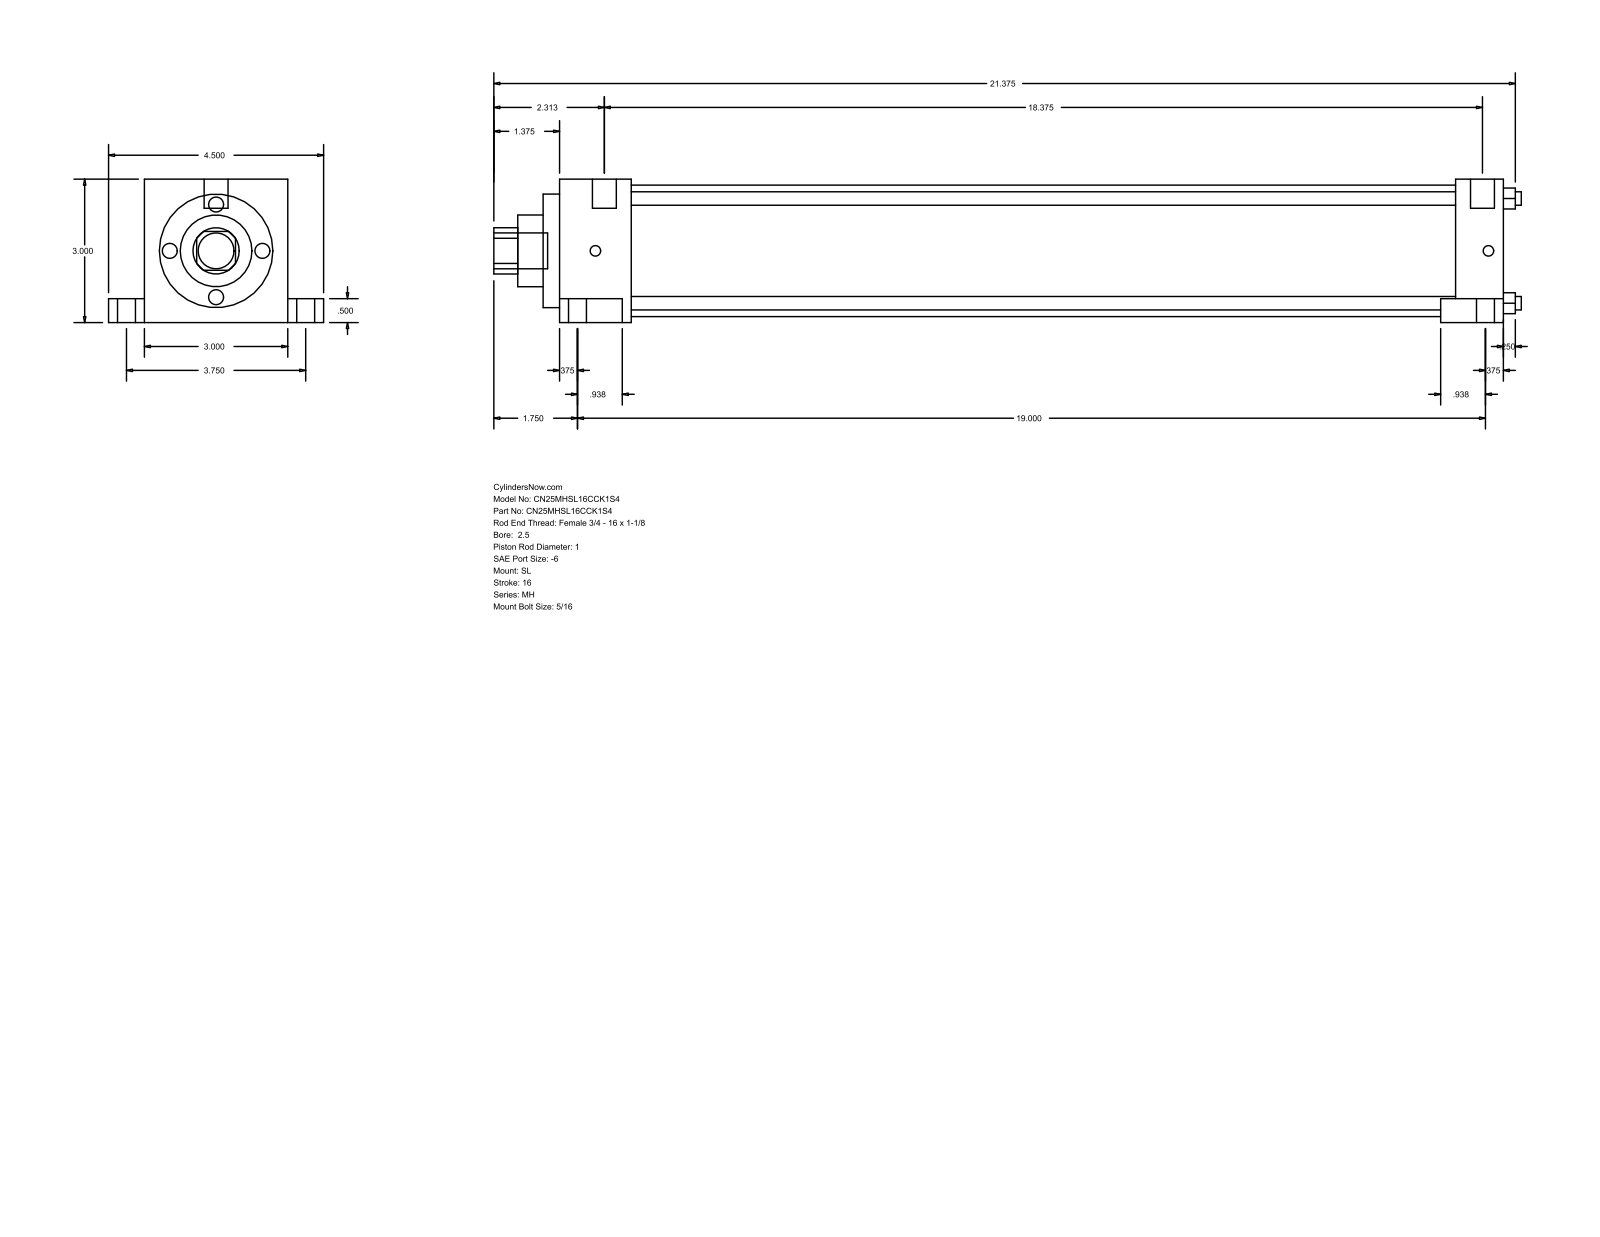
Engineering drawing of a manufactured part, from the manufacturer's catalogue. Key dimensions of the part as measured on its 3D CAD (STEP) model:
Part name (STEP PRODUCT): MH_SL__0250_1
STEP written by: GSSL Pune (CONFIG_CONTROL_DESIGN)
Units: millimetres
Bodies: 0 solids, 86 faces (61 planar, 25 cylindrical, 0 other)
Overall size (bounding box): 546.1 × 114.3 × 76.2
Round holes (diameter × count): ⌀7.14 ×4, ⌀25.4 ×1, ⌀38.1 ×1, ⌀60.33 ×1, ⌀69.85 ×1
Round bosses / shafts (diameter × count): ⌀15.88 ×2, ⌀9.53 ×2, ⌀5.56 ×2, ⌀19.05 ×1, ⌀12.7 ×1
Partial cylindrical surfaces — rounded edges, fillets, slot ends (radius × count): R12.29 ×1
Main face-to-face distances: 76.2, 25.4, 484.99, 510.39, 12.7, 63.5, 19.05, 95.25, 13.49, 498.48
Hole centre spacings: 39.33, 55.62, 78.66
